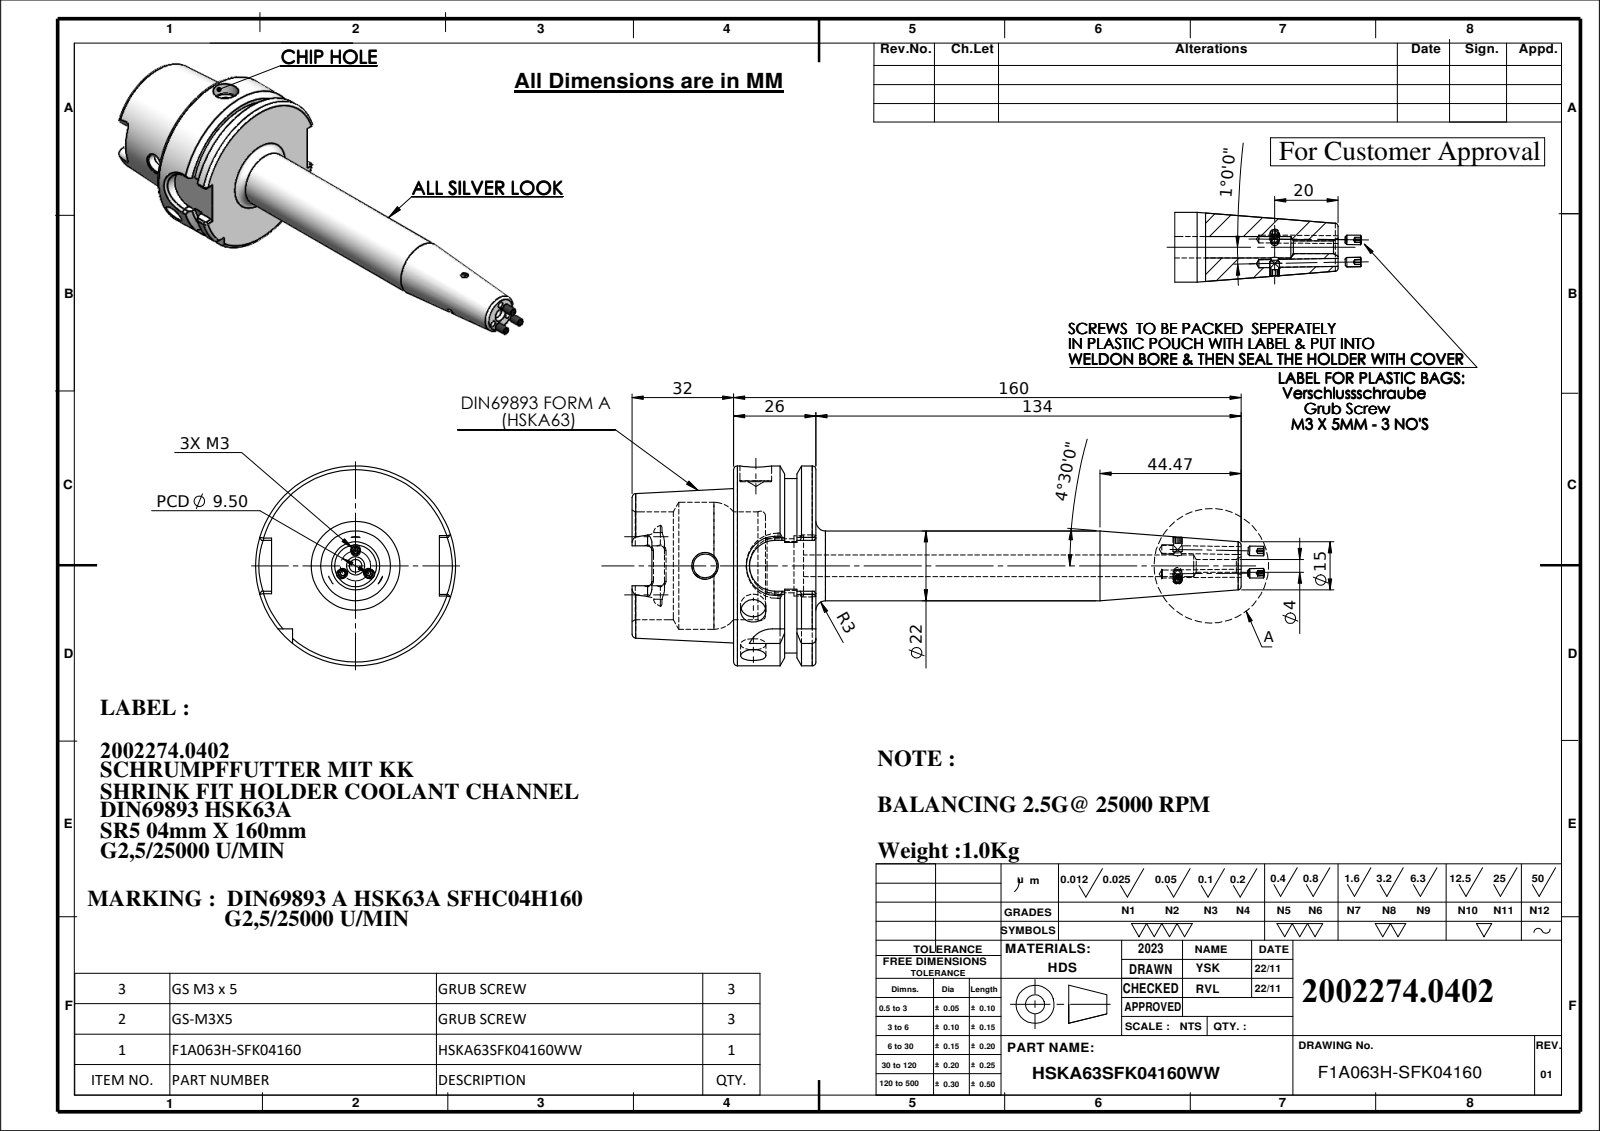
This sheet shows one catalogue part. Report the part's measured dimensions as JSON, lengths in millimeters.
{"part_name": "GS-M3X5; HSKA63SFK04160WW; socket set screw flat point_din_DIN 913 - M3 x 5-N; F1A063H-SFK04160", "step_written_by": "SolidWorks 2023 (CONFIG_CONTROL_DESIGN)", "units": "millimeters", "bodies": {"solids": 7, "faces": 305, "planar": 118, "cylindrical": 85, "other": 102}, "overall_size": [199.2, 63, 63], "volume_mm3": 122376, "surface_area_mm2": 34625, "round_holes": [[2.5, 6], [8, 2], [4, 1], [6.8, 1], [7.5, 1], [10, 1], [17, 1], [19, 1], [34, 1], [40, 1]], "round_bosses_or_shafts": [[3, 6], [63, 1], [55, 1], [22, 1]], "partial_cylinders_radius": [[1.3, 6], [2.88, 4], [8, 2], [9, 1]], "face_to_face_distances": [25.95, 10, 15.95, 32, 42, 57.95, 52.9, 54, 22, 12], "hole_center_spacings": [132.95]}
